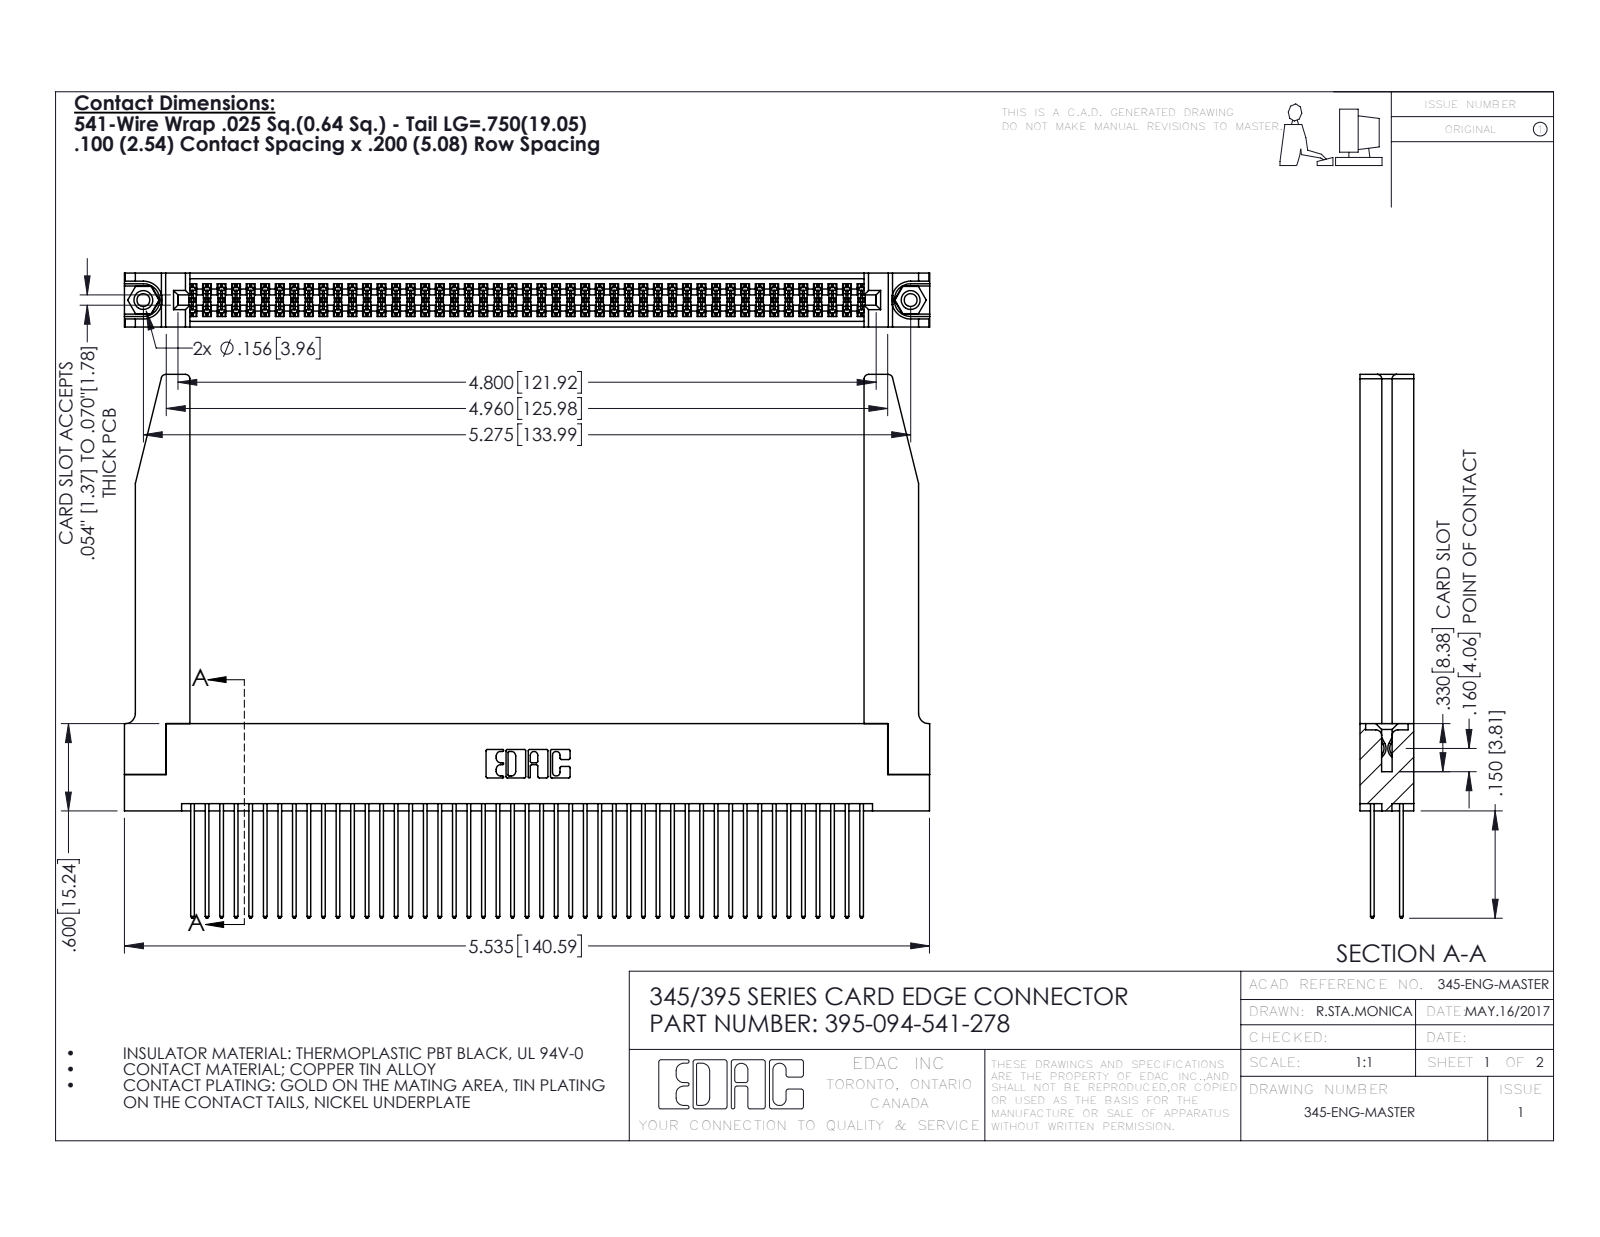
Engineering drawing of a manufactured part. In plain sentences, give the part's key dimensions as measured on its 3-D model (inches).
The part is named "395-094-541-278; 345-220-078_345-220-078; 345-292-001_345-293-141; 345 Part_Flush Mounting Lugs - 0.156 Dia-TH (+1 more)". Its 3-D file was written by "SolidWorks 2016 (CONFIG_CONTROL_DESIGN)". It is 99 solids with 5060 faces: 3324 planar, 1684 cylindrical and 52 other. Overall it measures 5.536 by 3.737 by 0.37 inches. Its volume is 1.343 cubic inches and its surface area 47.32 square inches. Round holes: 2 of diameter 0.089, 2 of diameter 0.125, 2 of diameter 0.156, 1 of diameter 0.064. Round bosses or shafts: 2 of diameter 0.155. Partial cylindrical surfaces (rounded edges, fillets, slot ends): 141 of radius 0.006, 94 of radius 0.01, 22 of radius 0.01, 8 of radius 0.03, 6 of radius 0.007, 6 of radius 0.031, 3 of radius 0.026, 2 of radius 0.014. The main face-to-face distances are 0.072, 0.298, 0.37, 0.2, 0.098, 0.272, 0.025, 0.225, 0.175, 0.148. The hole center spacings are 0.27, 5.039, 5.275.
